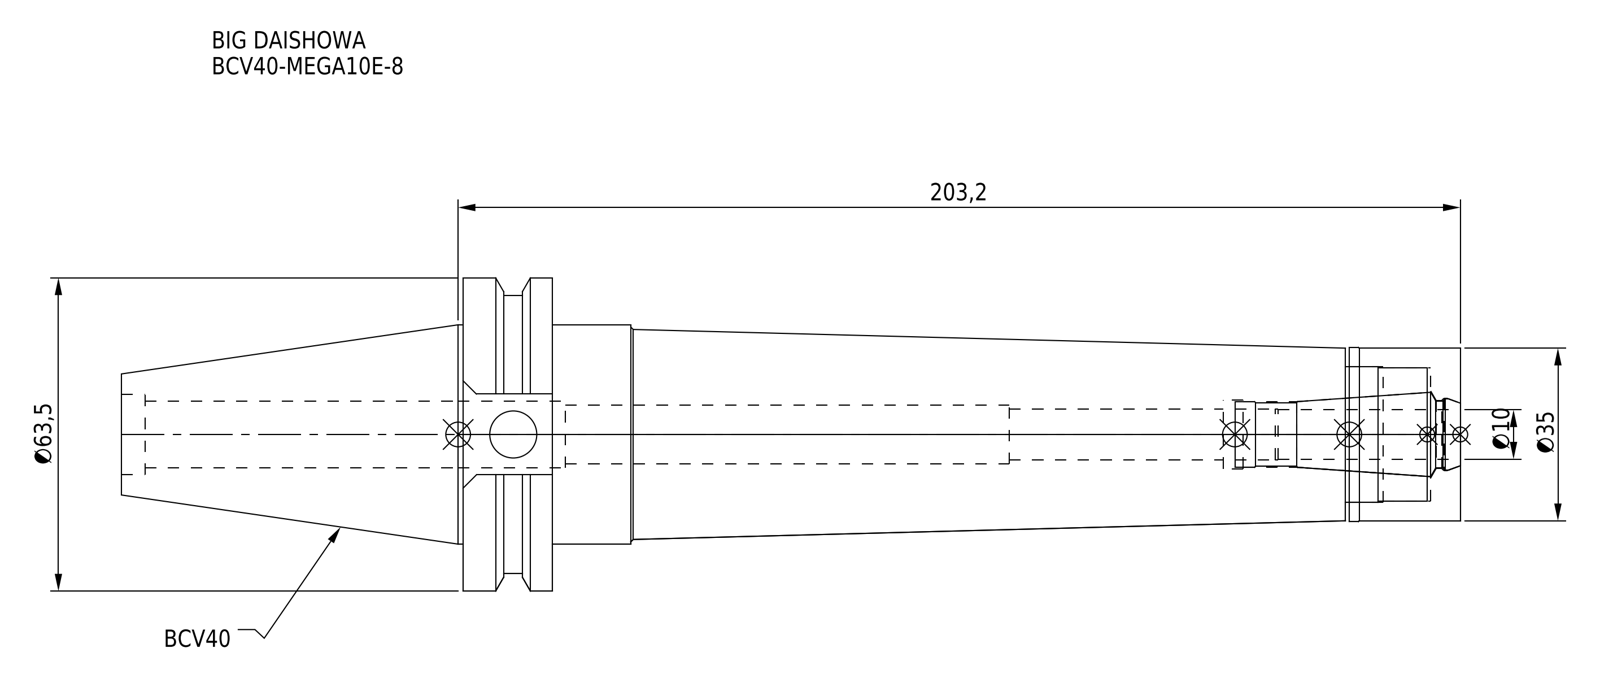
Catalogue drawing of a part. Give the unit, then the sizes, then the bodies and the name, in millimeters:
Units: millimetres
Overall size (bounding box): 271.45 × 63.5 × 61.35
Round holes (diameter × count): ⌀9.53 ×1, ⌀10.4 ×1, ⌀12 ×1, ⌀13.3 ×1, ⌀13.6 ×1, ⌀13.8 ×1, ⌀13.9 ×1, ⌀14.7 ×1, ⌀16.32 ×1, ⌀27 ×1, ⌀27.5 ×1
Round bosses / shafts (diameter × count): ⌀63.5 ×1, ⌀56.36 ×1, ⌀44.45 ×1, ⌀35.3 ×1, ⌀35 ×1
Main face-to-face distances: 18.05, 184.15, 202.2, 6, 22.5, 161.65, 179.7, 23.3, 0.8, 160.85
Volume: 300 014 mm³ · Surface area: 53 946 mm²
Bodies: 2 solids, 93 faces (31 planar, 42 cylindrical, 20 other)
Part name (STEP PRODUCT): BCV40-MEGA10E-8_1.stp; BCV40ME10080-010_ASM.stp; DXF_TEMP_ASSY_ASM_4_ASM.stp; BCV40-MEGA10E-8-100-FreeParts (+3 more)
STEP written by: SolidWorks 2019 (CONFIG_CONTROL_DESIGN)
